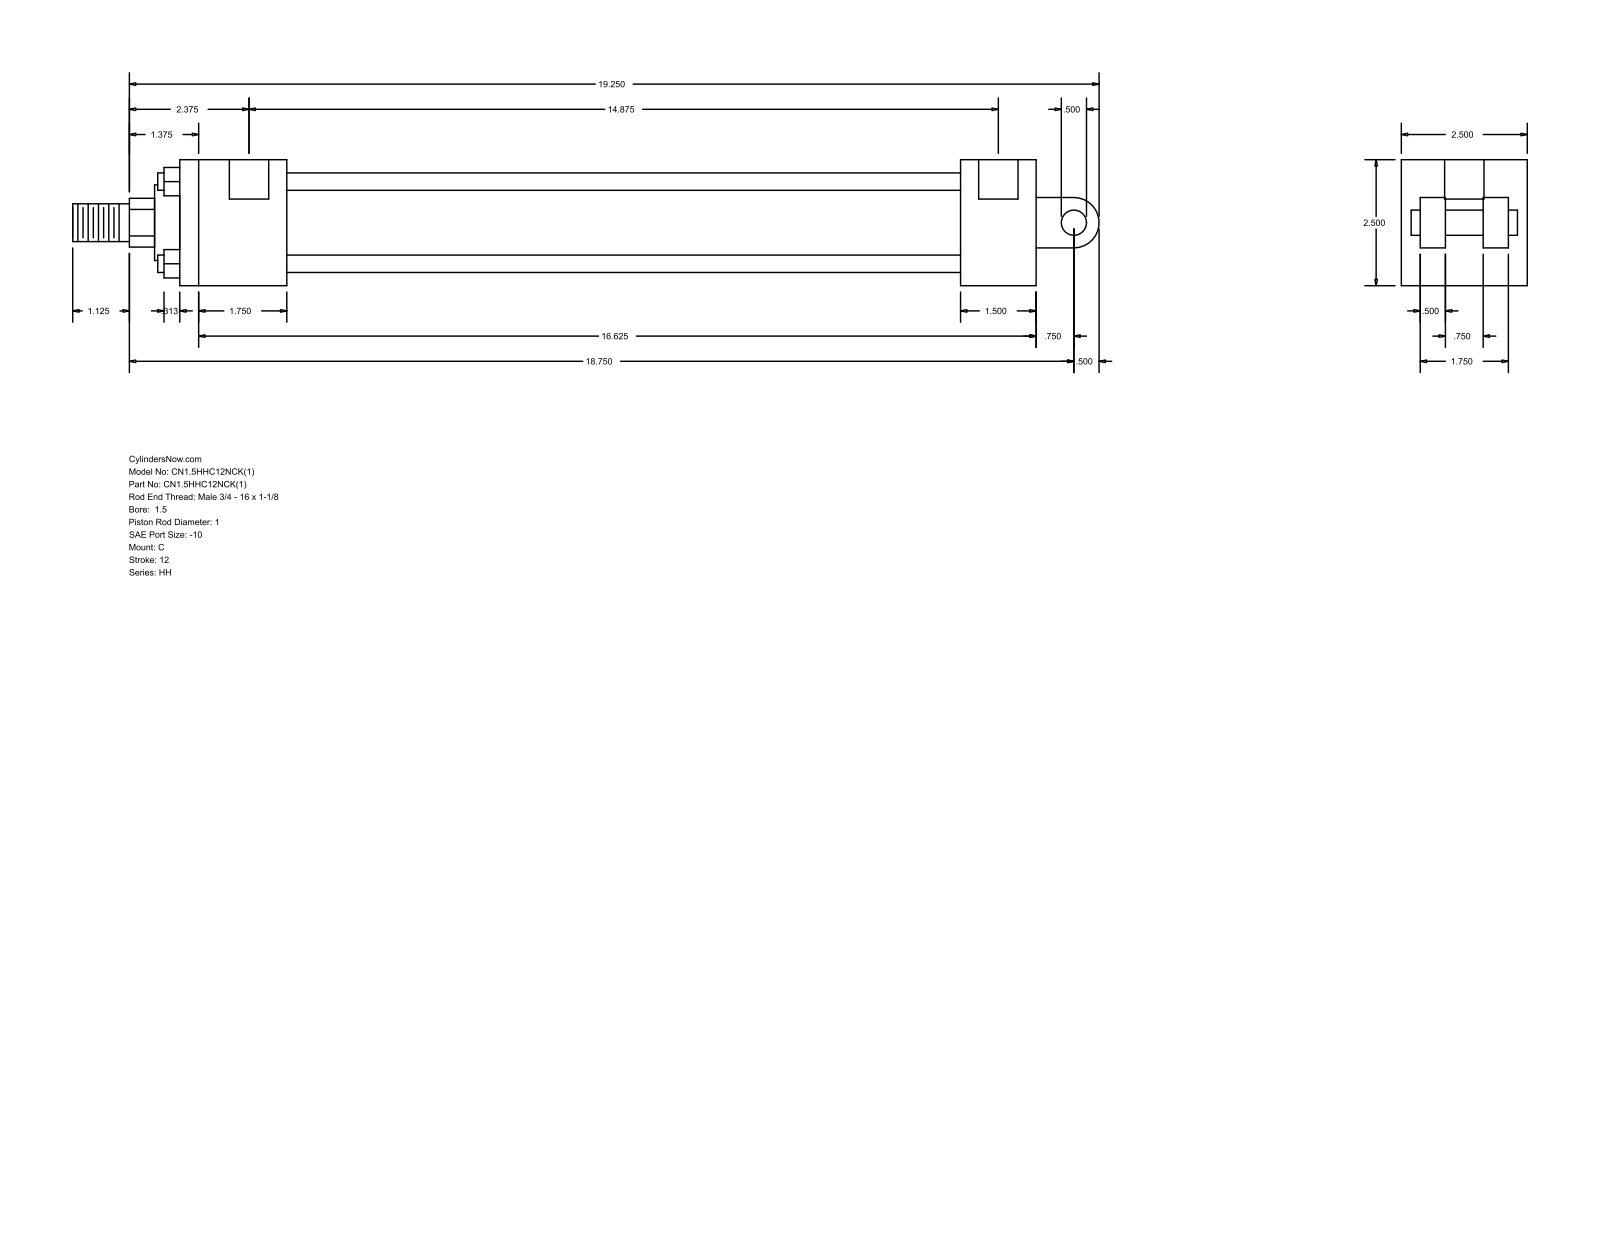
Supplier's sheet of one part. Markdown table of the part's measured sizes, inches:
| quantity | value |
| --- | --- |
| part name | HH_C__0150_1 |
| STEP written by | GSSL Pune (CONFIG_CONTROL_DESIGN) |
| units | inches |
| bodies | 0 solids, 99 faces (70 planar, 29 cylindrical, 0 other) |
| overall size | 20.375 × 2.5 × 2.5 |
| round holes (diameter × count) | 0.219 × 4, 0.781 × 2 |
| round bosses / shafts (diameter × count) | 0.345 × 4, 1.75 × 1, 1.5 × 1, 1 × 1, 0.75 × 1, 0.5 × 1 |
| partial cylindrical surfaces (radius × count) | 0.484 × 1, 0.5 × 1 |
| main face-to-face distances | 2.5, 2.125, 1.5, 13.375, 14.875, 15.5, 17, 0.5, 0.875, 1.625 |
| hole center spacings | 0.063, 14.937, 15, 14.875 |
